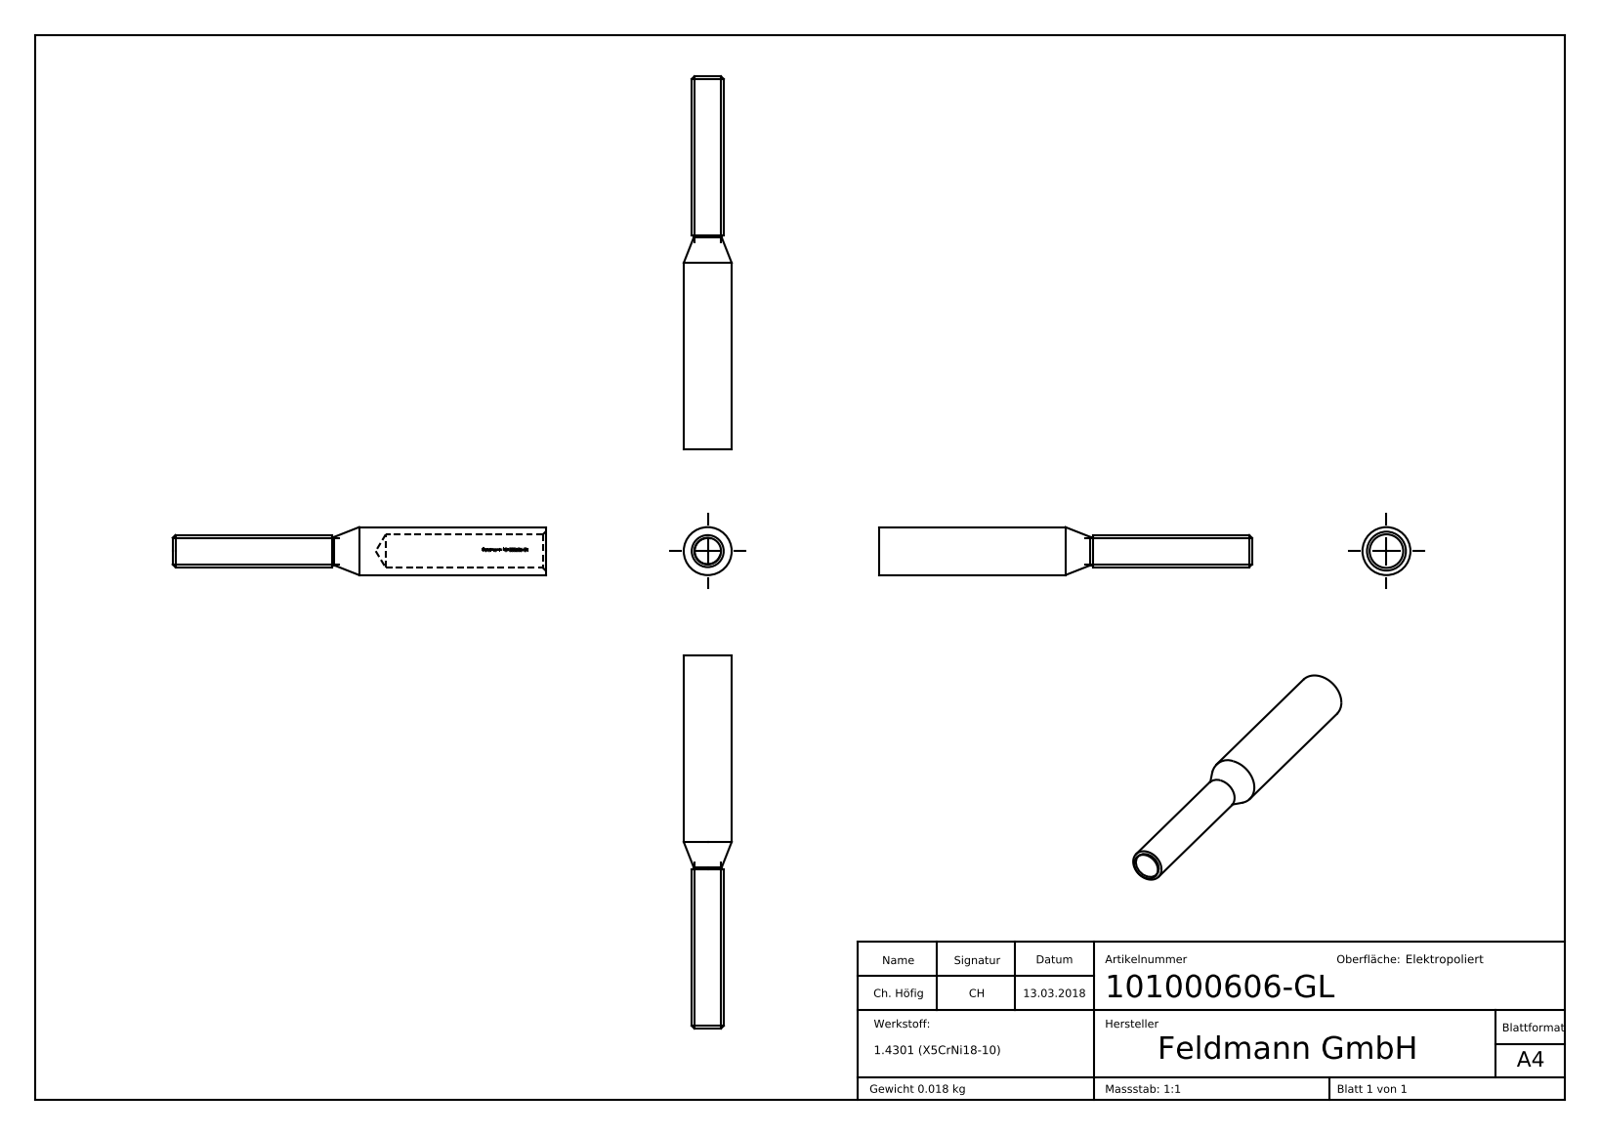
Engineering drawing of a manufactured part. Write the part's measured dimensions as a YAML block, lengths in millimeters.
part_name: "101000606-GL"
step_written_by: "SolidWorks 2015 (CONFIG_CONTROL_DESIGN)"
units: millimeters
bodies: {solids: 1, faces: 255, planar: 89, cylindrical: 38, other: 128}
overall_size: [70, 9, 9]
volume: 2314
surface_area: 2364
round_holes:
  - {diameter: 6.3, count: 1}
round_bosses_or_shafts:
  - {diameter: 9, count: 1}
  - {diameter: 6, count: 1}
  - {diameter: 5.3, count: 1}
partial_cylinders:
  - {radius: 3.25, count: 1}
face_to_face_distances: [70, 40.1, 29.9, 7.5, 3.07, 0.82, 3.89, 4.43, 3.61, 8.31]
